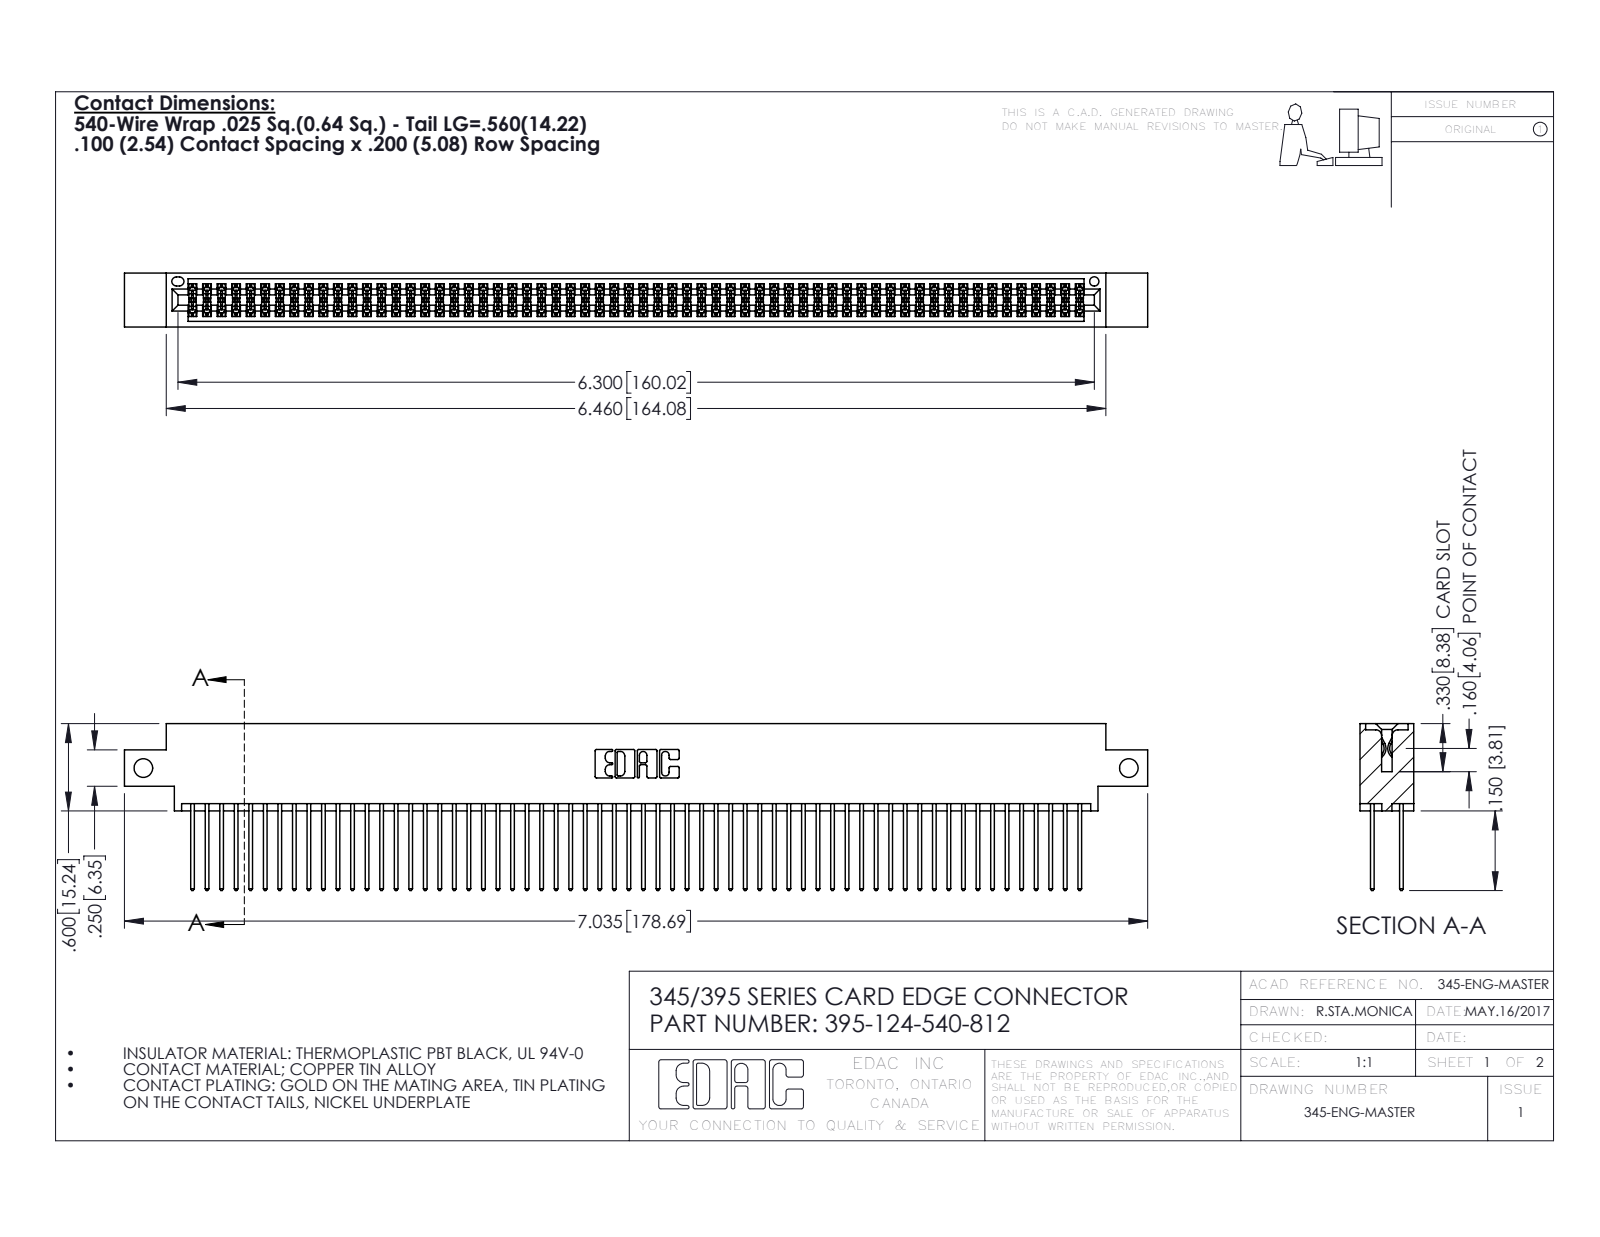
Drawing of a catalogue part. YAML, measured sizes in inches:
part_name: "345-292-001_345-293-140; 345 Part_0.170 Offset - Side Mount; 395-124-540-812"
step_written_by: "SolidWorks 2016 (CONFIG_CONTROL_DESIGN)"
units: inches
bodies: {solids: 125, faces: 6330, planar: 4176, cylindrical: 2154, other: 0}
overall_size: [7.035, 1.147, 0.37]
volume: 1.087
surface_area: 44.81
round_holes:
  - {diameter: 0.128, count: 2}
  - {diameter: 0.064, count: 1}
partial_cylinders:
  - {radius: 0.006, count: 186}
  - {radius: 0.01, count: 124}
  - {radius: 0.01, count: 22}
  - {radius: 0.007, count: 6}
  - {radius: 0.031, count: 6}
  - {radius: 0.026, count: 3}
  - {radius: 0.014, count: 2}
  - {radius: 0.019, count: 2}
face_to_face_distances: [0.072, 0.298, 0.2, 0.098, 0.272, 0.025, 0.37, 0.225, 0.175, 0.149]
hole_center_spacings: [6.775]
